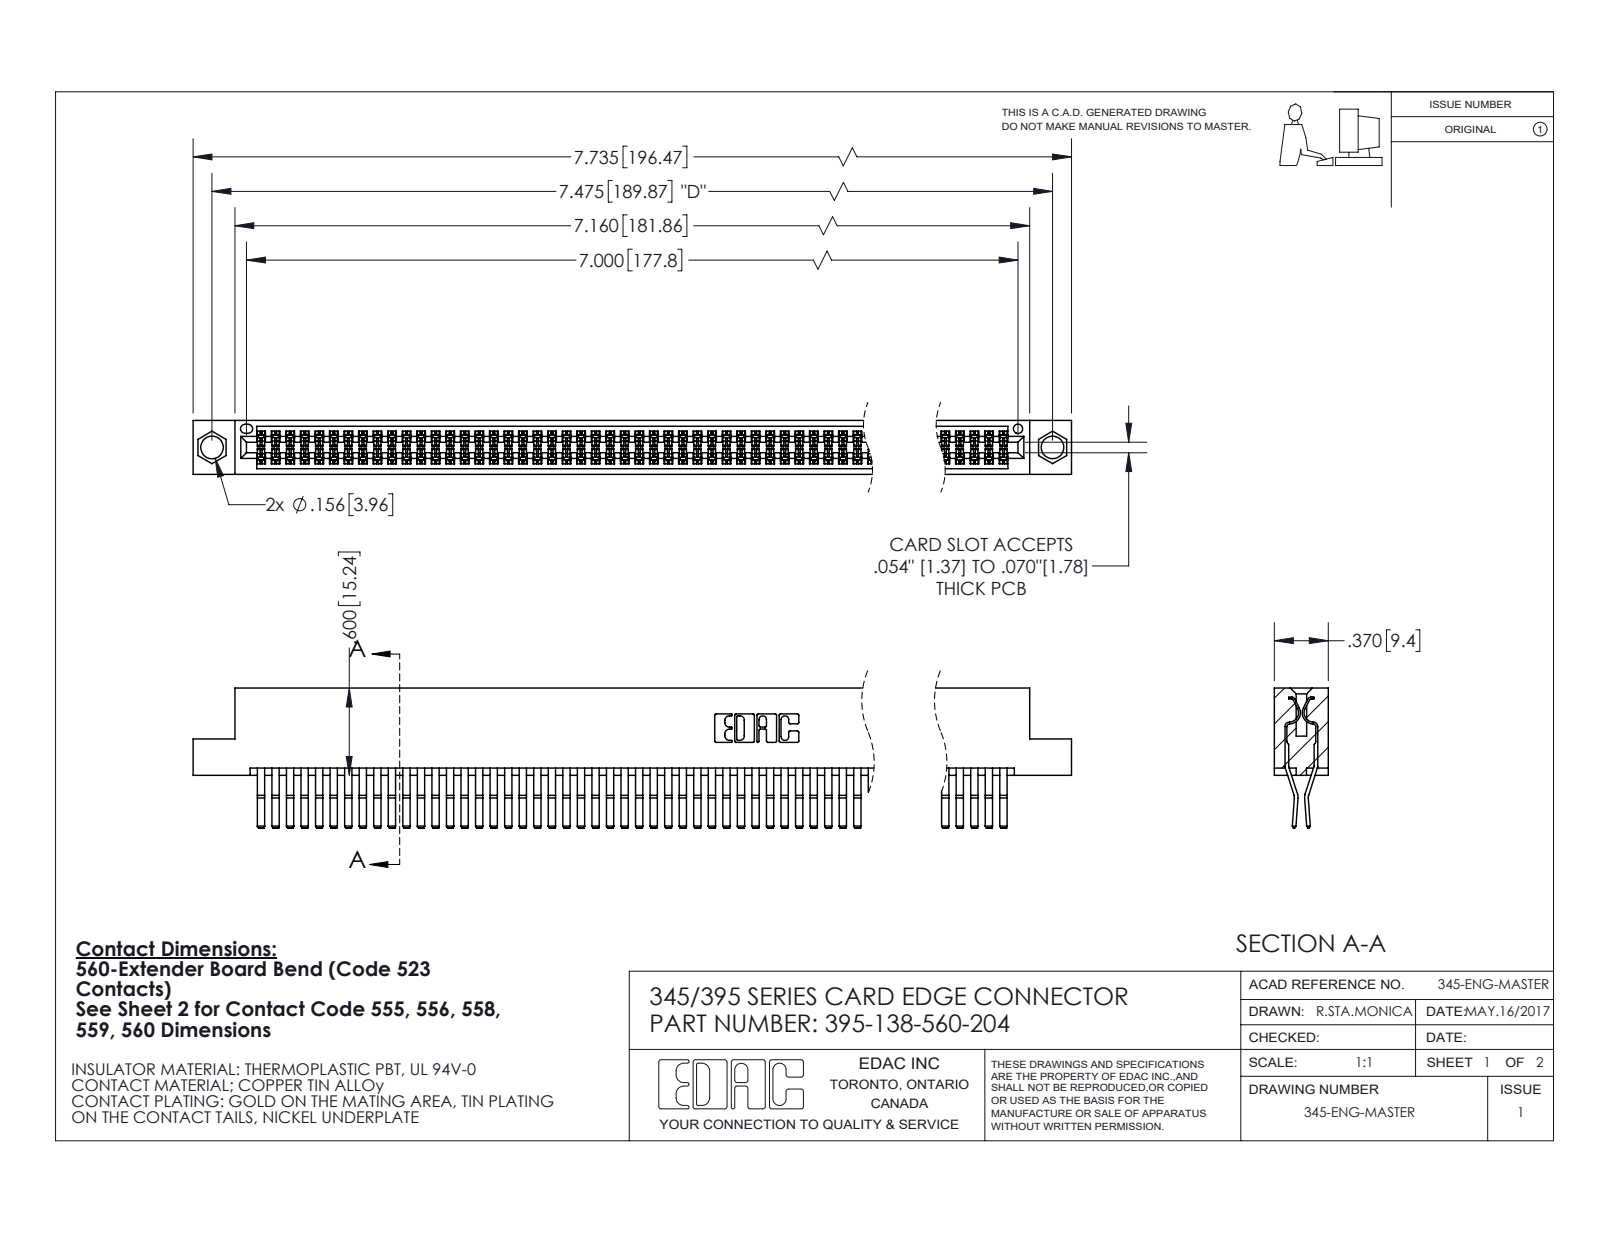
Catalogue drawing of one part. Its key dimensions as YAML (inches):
part_name: "345-292-001_560 Tail; 395-138-560-204; 345 Part_Flush Mounting Lugs - 0.156 Dia-TI"
step_written_by: "SolidWorks 2020 (CONFIG_CONTROL_DESIGN)"
units: inches
bodies: {solids: 139, faces: 7316, planar: 4648, cylindrical: 2668, other: 0}
overall_size: [7.735, 0.962, 0.37]
volume: 1.229
surface_area: 50.32
round_holes:
  - {diameter: 0.156, count: 2}
  - {diameter: 0.064, count: 1}
partial_cylinders:
  - {radius: 0.006, count: 207}
  - {radius: 0.01, count: 22}
  - {radius: 0.007, count: 6}
  - {radius: 0.031, count: 6}
  - {radius: 0.026, count: 3}
  - {radius: 0.01, count: 2}
  - {radius: 0.014, count: 2}
  - {radius: 0.019, count: 2}
face_to_face_distances: [0.025, 0.298, 0.072, 0.37, 0.2, 0.098, 0.272, 0.225, 0.175, 0.149]
hole_center_spacings: [0.27, 7.239, 7.475]
